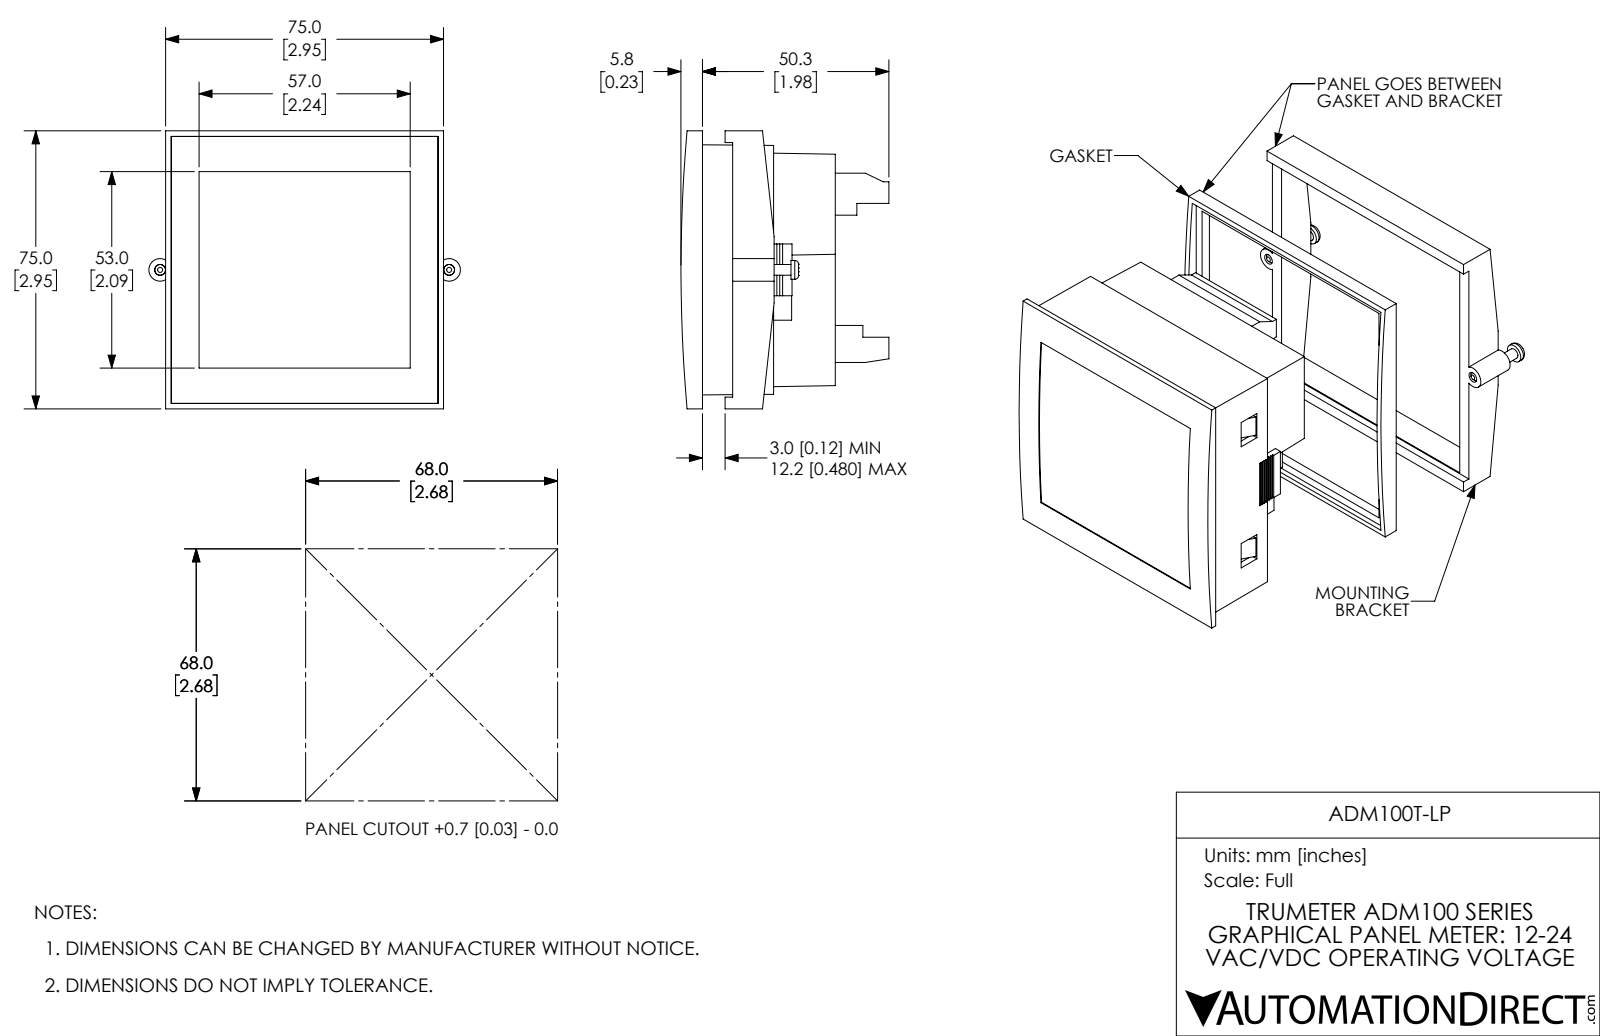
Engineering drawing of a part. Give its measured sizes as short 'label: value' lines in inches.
name: ADM100T-LP
written by: SolidWorks 2021 (CONFIG_CONTROL_DESIGN)
unit: in
bodies: 23 solids, 419 faces (335 planar, 76 cylindrical, 8 other)
size: 3.311 × 2.953 × 2.209
volume: 9.565 in³; area: 90.64 in²
holes: 13× ⌀0.151, 2× ⌀0.115
bosses: 13× ⌀0.148, 2× ⌀0.2, 2× ⌀0.114
rounds: 2× R0.12, 2× R17.037
face distances: 0.075, 0.305, 0.236, 2.717, 2.657, 0.089, 0.148, 2.805, 2.583, 1.142
hole spacings: 1.653, 0.2, 1.677, 0.4, 1.724, 0.6, 1.792, 0.8
